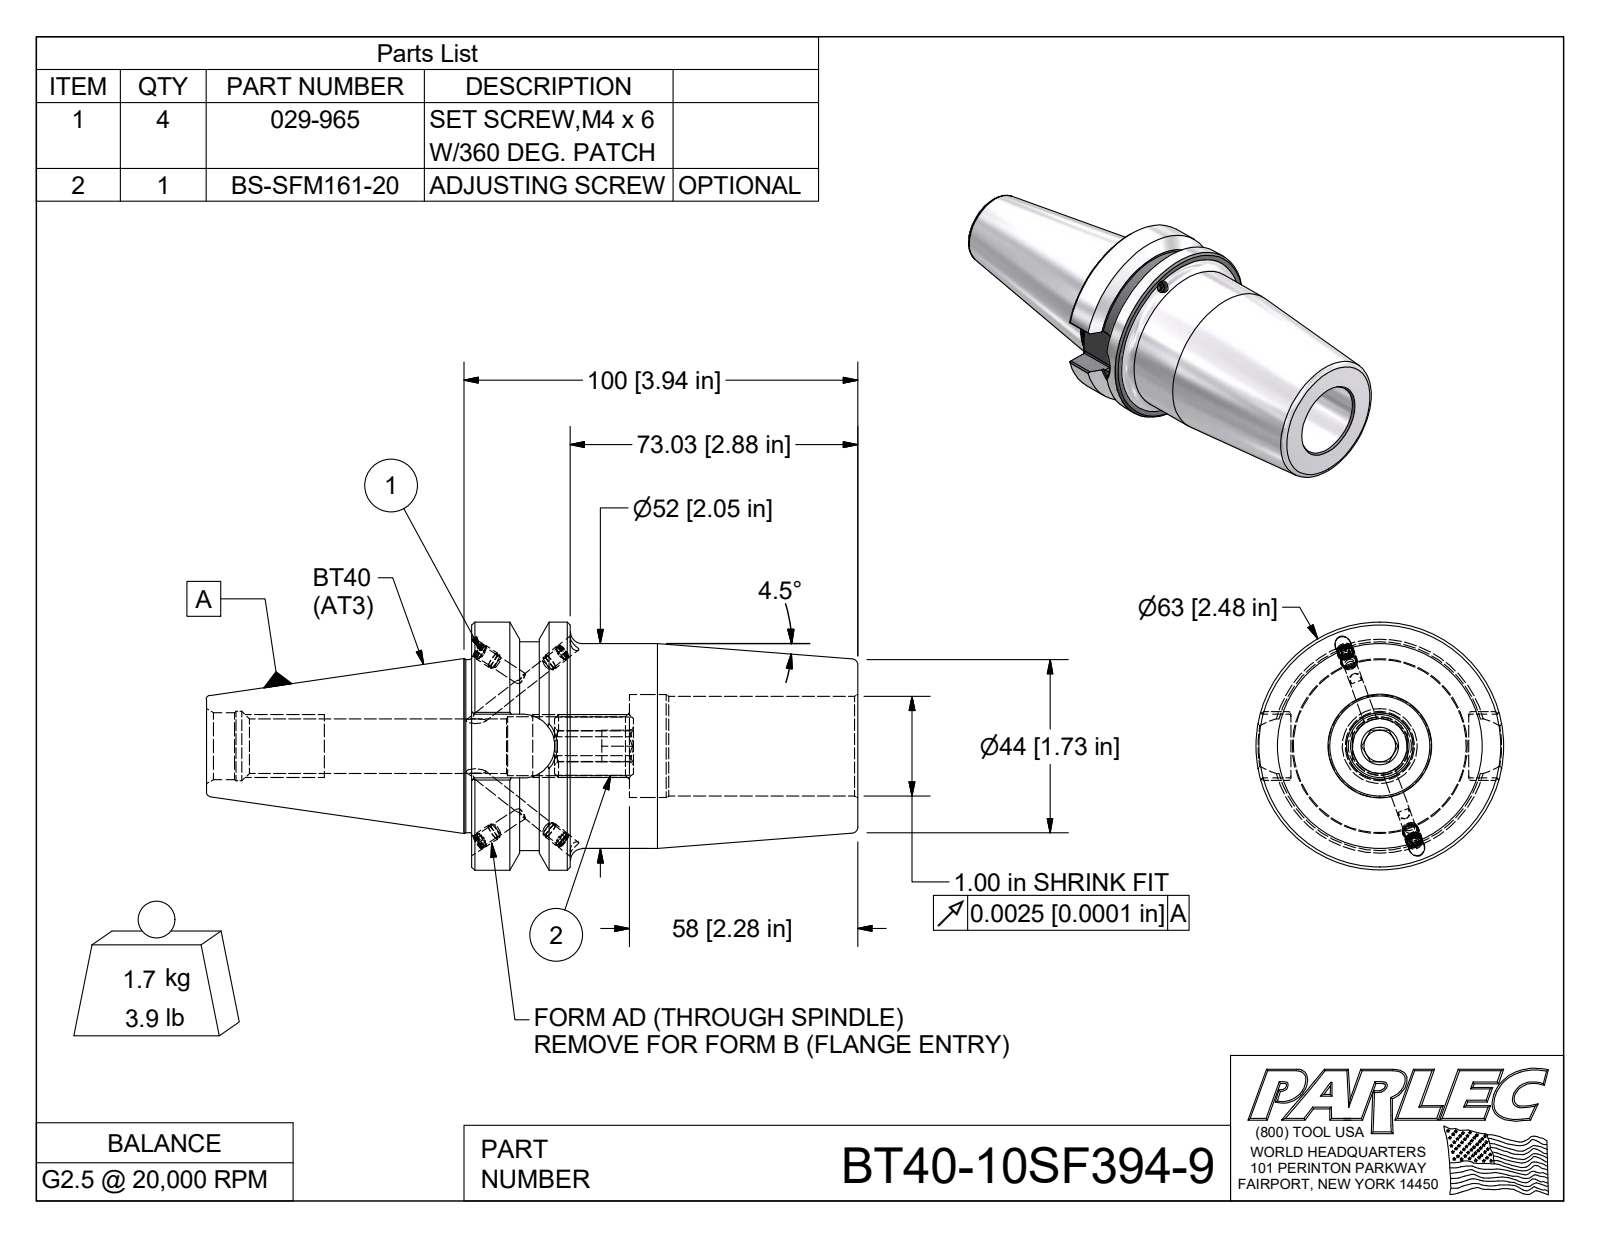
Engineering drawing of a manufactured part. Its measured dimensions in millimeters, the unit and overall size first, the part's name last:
Units: millimetres
Overall size (bounding box): 165.4 × 63 × 63
Round holes (diameter × count): ⌀3.3 ×4, ⌀4.1 ×4, ⌀17.6 ×1, ⌀25.4 ×1, ⌀26.1 ×1
Round bosses / shafts (diameter × count): ⌀4.2 ×4, ⌀4 ×4, ⌀63 ×1, ⌀53 ×1, ⌀52 ×1, ⌀44.5 ×1, ⌀43.9 ×1
Partial cylindrical surfaces — rounded edges, fillets, slot ends (radius × count): R0.5 ×8, R8 ×1, R8.1 ×1
Main face-to-face distances: 98, 25, 73, 40, 15, 58, 15.6, 29.6, 45.2, 67.4
Volume: 228 400 mm³ · Surface area: 41 180 mm²
Bodies: 6 solids, 173 faces (79 planar, 43 cylindrical, 51 other)
Part name (STEP PRODUCT): BT40-10SF394-9; BT40BC-10SF394-9-1; 029-965; BS-SFM161-20
STEP written by: Autodesk Inventor 2009 (AUTOMOTIVE_DESIGN)
